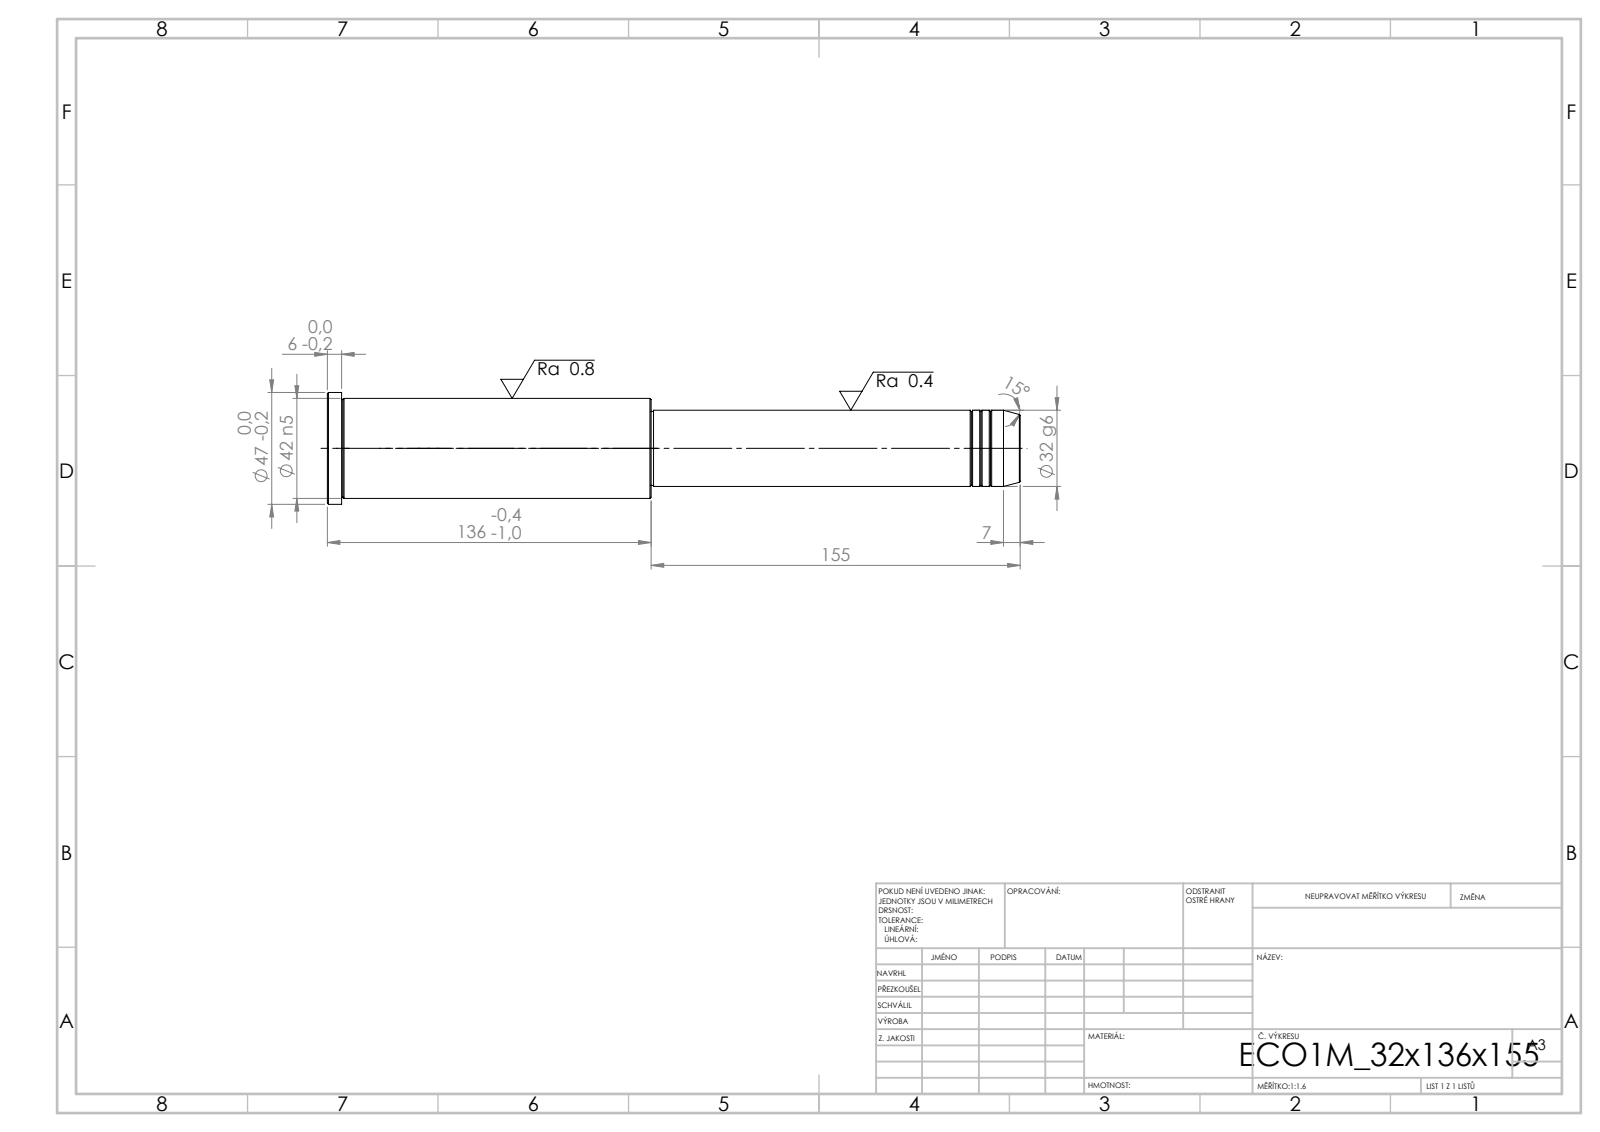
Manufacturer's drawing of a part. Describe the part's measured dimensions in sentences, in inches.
Its 3-D file was written by "SolidWorks 2019 (CONFIG_CONTROL_DESIGN)". It is 1 solid with 43 faces: 5 planar, 14 cylindrical and 24 other. Overall it measures 11.457 by 1.85 by 1.85 inches. Its volume is 19.18 cubic inches and its surface area 57.56 square inches. Round bosses or shafts: 1 of diameter 1.85, 1 of diameter 1.654, 1 of diameter 1.26, 1 of diameter 1.22. The main face-to-face distances are 11.457, 6.102, 5.354, 11.22, 5.118, 0.236, 6.063, 0.039, 5.157, 5.394.
